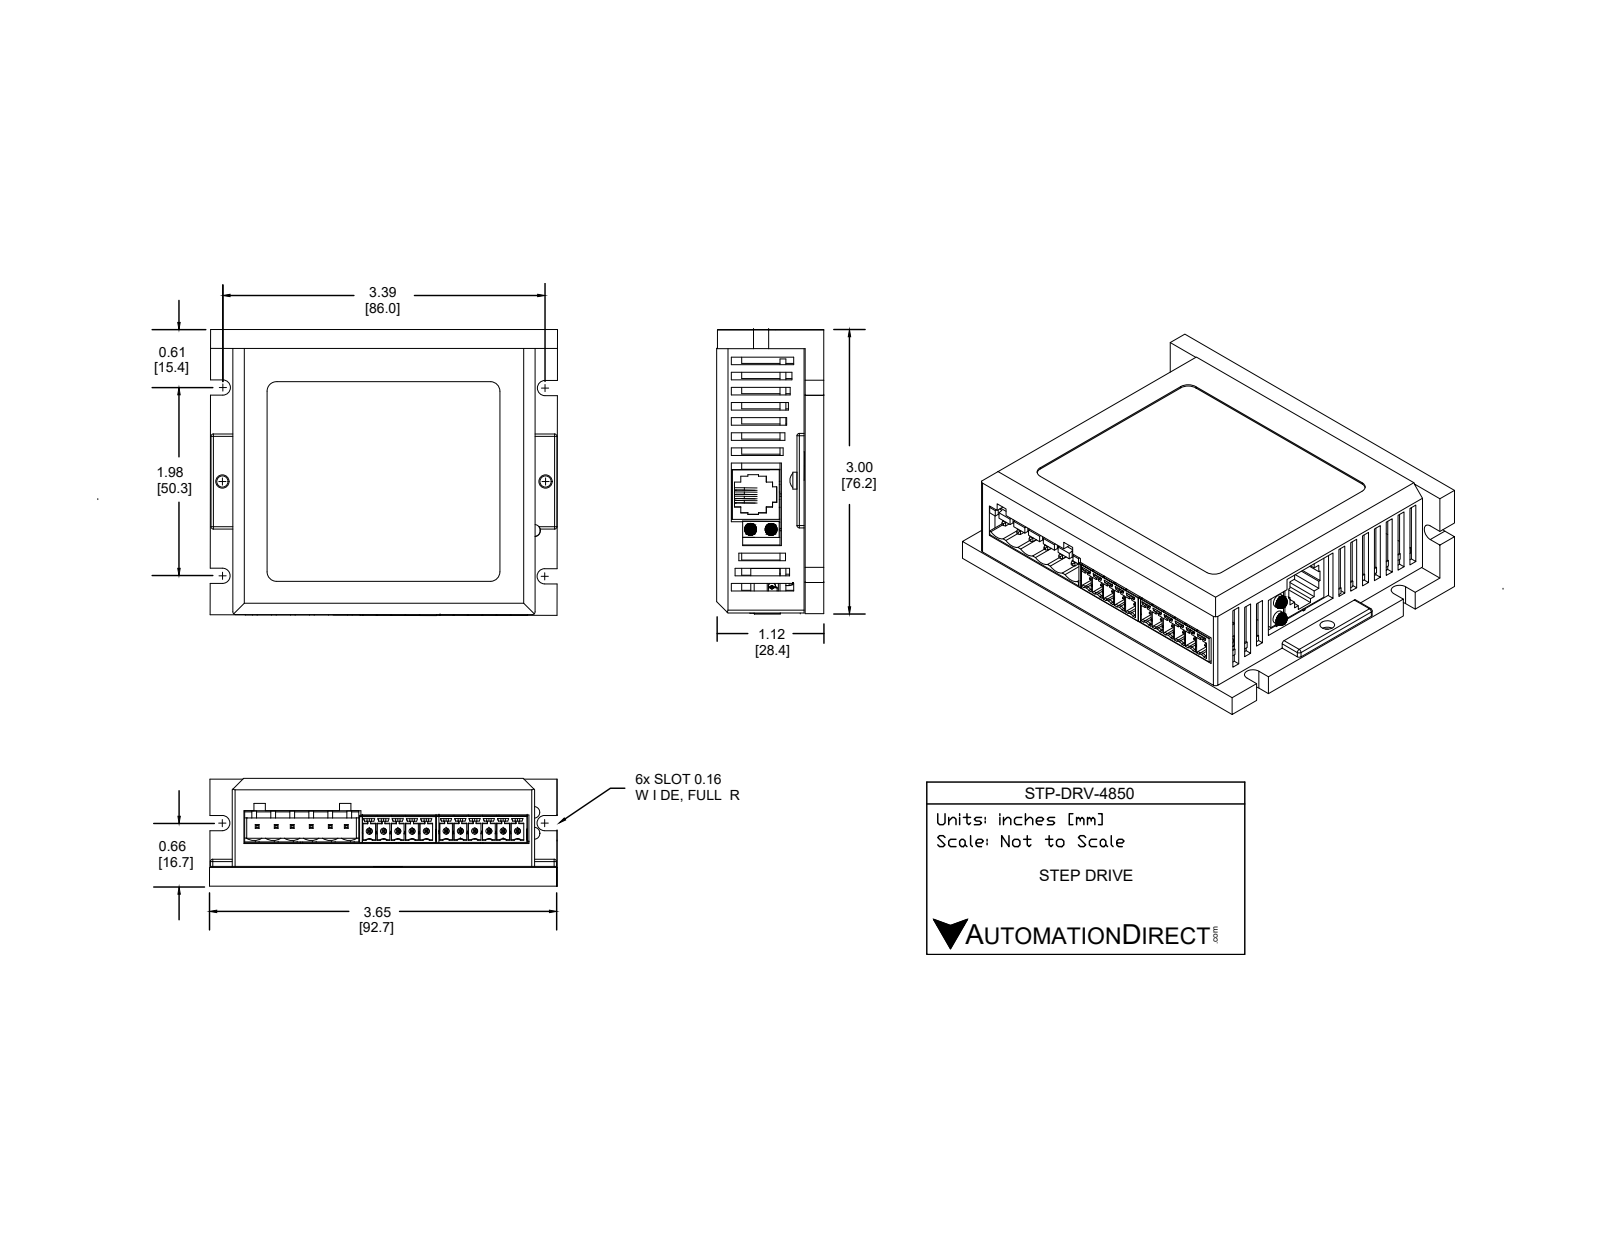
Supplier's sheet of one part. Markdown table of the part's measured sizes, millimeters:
| quantity | value |
| --- | --- |
| part name | LED_ASSY; LED_GRN; Conn_phoenix_power_6Pin; LED_RED (+8 more) |
| STEP written by | SolidWorks 2014 (AUTOMOTIVE_DESIGN) |
| units | millimeters |
| bodies | 15 solids, 1430 faces (1107 planar, 276 cylindrical, 47 other) |
| overall size | 92.8 × 76.4 × 28.8 |
| volume | 73 760 mm³ |
| surface area | 59 640 mm² |
| round holes (diameter × count) | 1.2 × 11, 2.8 × 4, 3 × 2, 3.6 × 2, 4 × 2, 2.5 × 1, 4.8 × 1 |
| round bosses / shafts (diameter × count) | 1.6 × 11, 1.2 × 11, 3.2 × 2, 0.5 × 2, 7.6 × 1 |
| partial cylindrical surfaces (radius × count) | 0.2 × 25, 0.2 × 20, 1.5 × 11, 0.2 × 8, 0.6 × 8, 2 × 6, 3.8 × 6, 0.1 × 4 |
| main face-to-face distances | 5, 6.8, 11.8, 10.2, 1.6, 5.2, 26.9, 21.9, 16.7, 15.1 |
| hole center spacings | 3.8, 7.6, 11.4, 15.2, 86.4, 0.4, 0.5, 0.5 |
